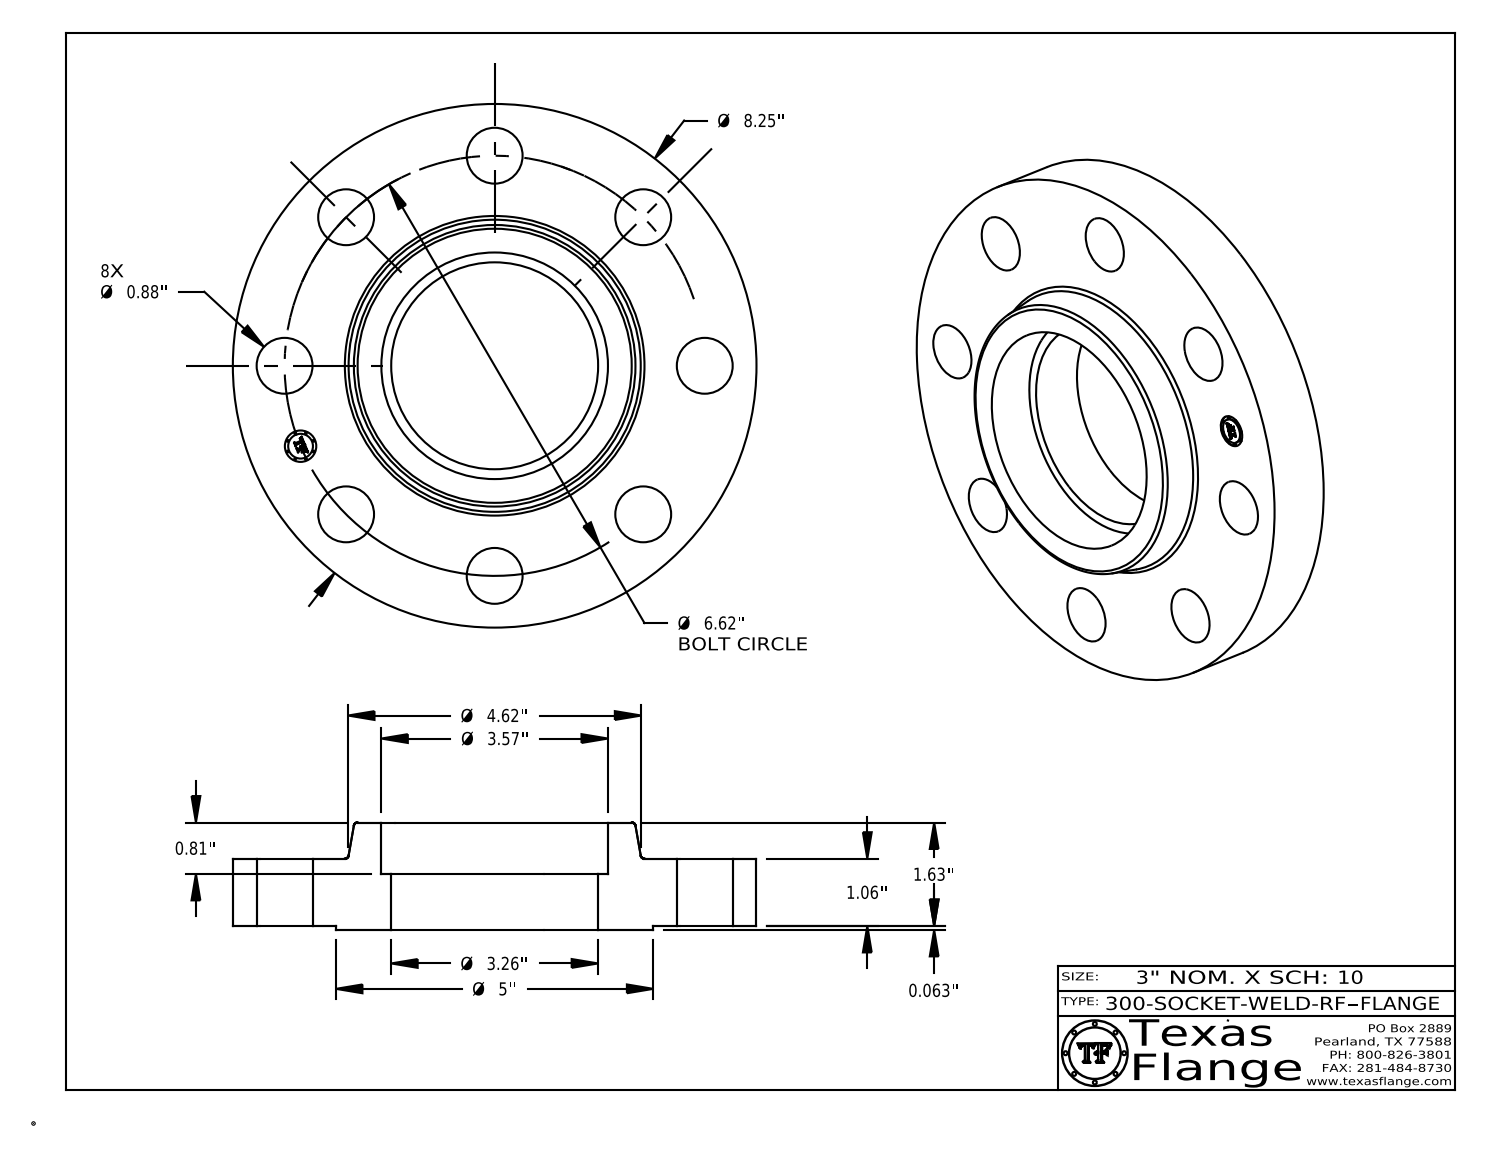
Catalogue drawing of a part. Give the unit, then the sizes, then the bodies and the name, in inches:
Units: inches
Overall size (bounding box): 8.25 × 8.25 × 1.693
Round holes (diameter × count): ⌀0.88 ×8, ⌀0.495 ×1, ⌀3.26 ×1, ⌀3.57 ×1
Round bosses / shafts (diameter × count): ⌀0.03 ×8, ⌀8.25 ×1, ⌀5 ×1, ⌀0.39 ×1
Main face-to-face distances: 1.06, 0.063, 1.122, 1.693, 1.63, 0.57, 0.883, 0.82, 0.24, 0.81
Hole centre spacings: 3.31, 2.533, 6.116, 4.681, 4.681, 1.291, 3.678, 6.493
Volume: 46.4 in³ · Surface area: 156.9 in²
Bodies: 1 solid, 420 faces (370 planar, 44 cylindrical, 6 other)
Part name (STEP PRODUCT): 300-SOCKET-WELD-RF
STEP written by: CATIA V5 STEP AP214 (AUTOMOTIVE_DESIGN)
